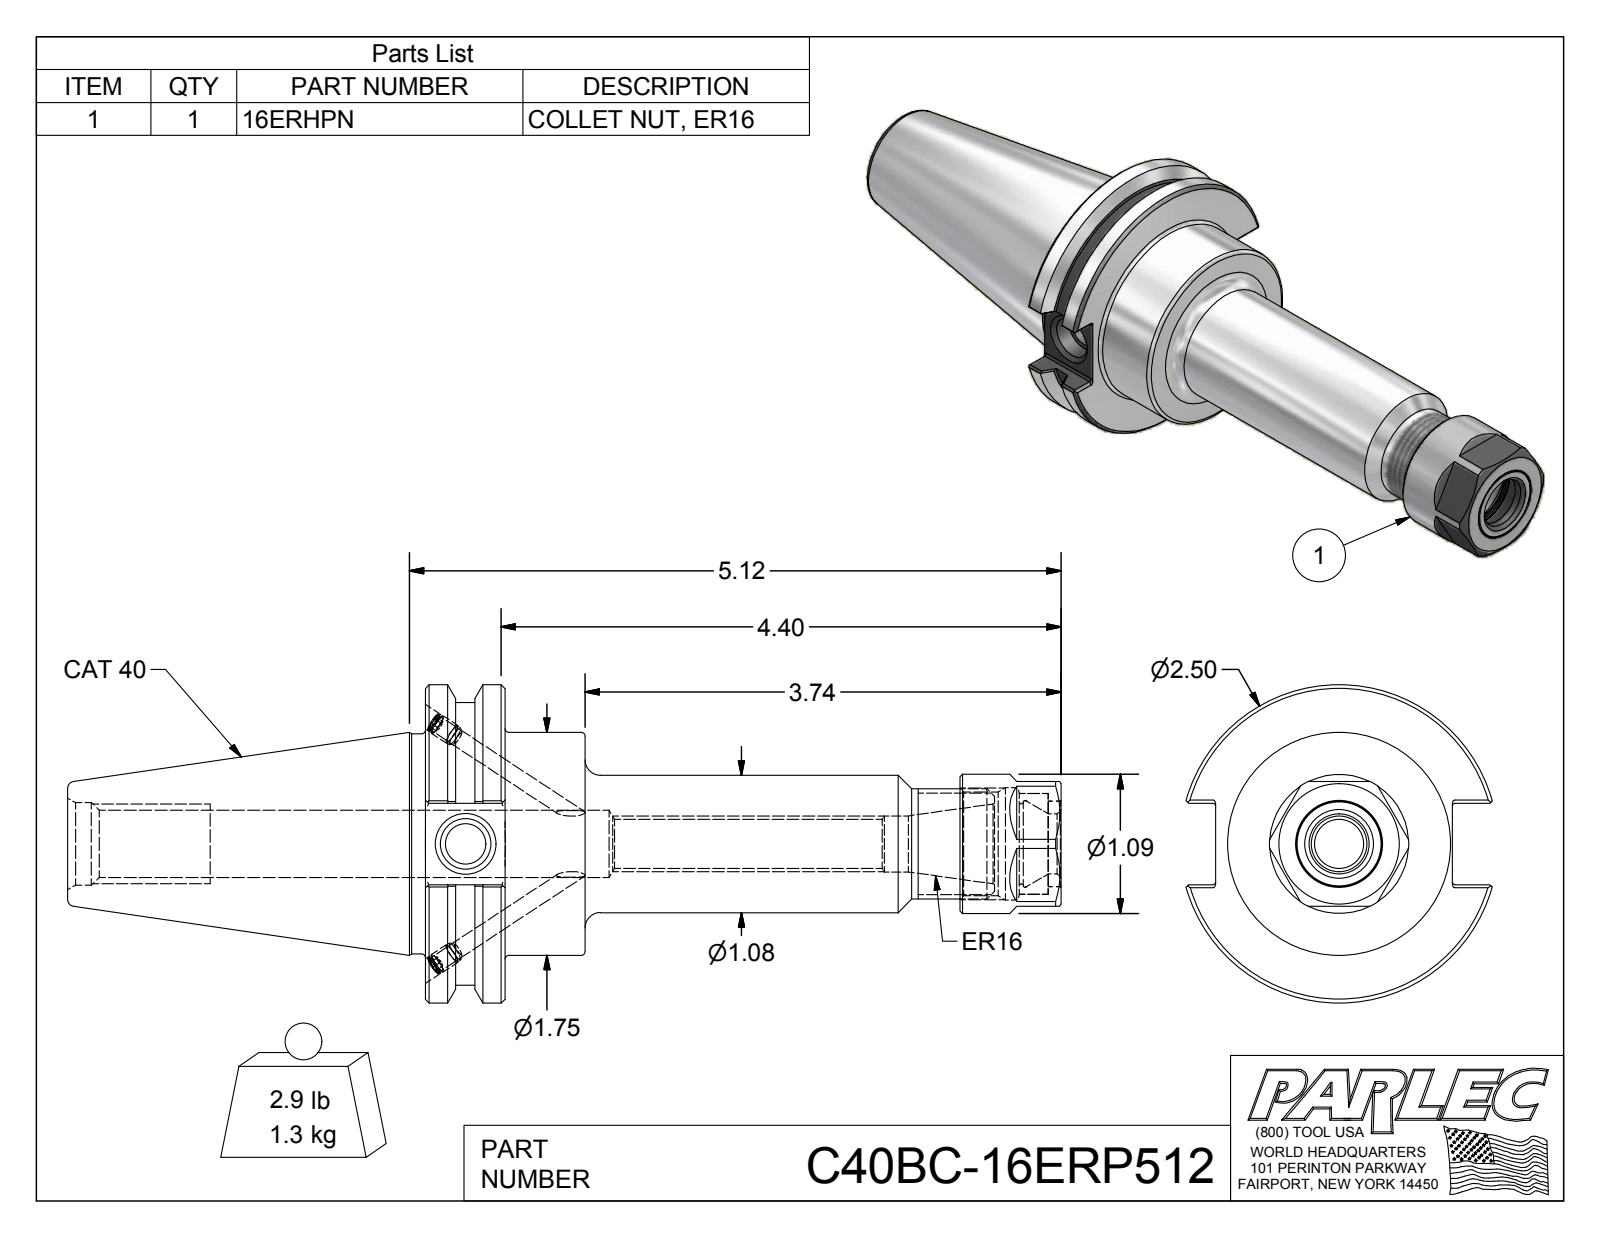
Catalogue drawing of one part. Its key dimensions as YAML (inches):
part_name: "C40BC-16ERP512; C40BCB-16ER5-1; 029-965; 16ERHPN"
step_written_by: "Autodesk Inventor 2012 (AUTOMOTIVE_DESIGN)"
units: inches
bodies: {solids: 5, faces: 174, planar: 74, cylindrical: 48, other: 52}
overall_size: [7.807, 2.5, 2.406]
volume: 10.08
surface_area: 58.95
round_holes:
  - {diameter: 0.13, count: 2}
  - {diameter: 0.161, count: 2}
  - {diameter: 0.315, count: 1}
  - {diameter: 0.383, count: 1}
  - {diameter: 0.399, count: 1}
  - {diameter: 0.44, count: 1}
  - {diameter: 0.474, count: 1}
  - {diameter: 0.527, count: 1}
  - {diameter: 0.63, count: 1}
  - {diameter: 0.648, count: 1}
  - {diameter: 0.674, count: 1}
  - {diameter: 0.68, count: 1}
round_bosses_or_shafts:
  - {diameter: 0.165, count: 2}
  - {diameter: 0.157, count: 2}
  - {diameter: 2.5, count: 1}
  - {diameter: 2.219, count: 1}
  - {diameter: 1.75, count: 1}
  - {diameter: 1.73, count: 1}
  - {diameter: 1.092, count: 1}
  - {diameter: 1.08, count: 1}
partial_cylinders:
  - {radius: 0.02, count: 12}
face_to_face_distances: [0.625, 1.255, 0.63, 0.98, 4.995, 4.37, 3.74, 0.17, 0.81, 4.199]
